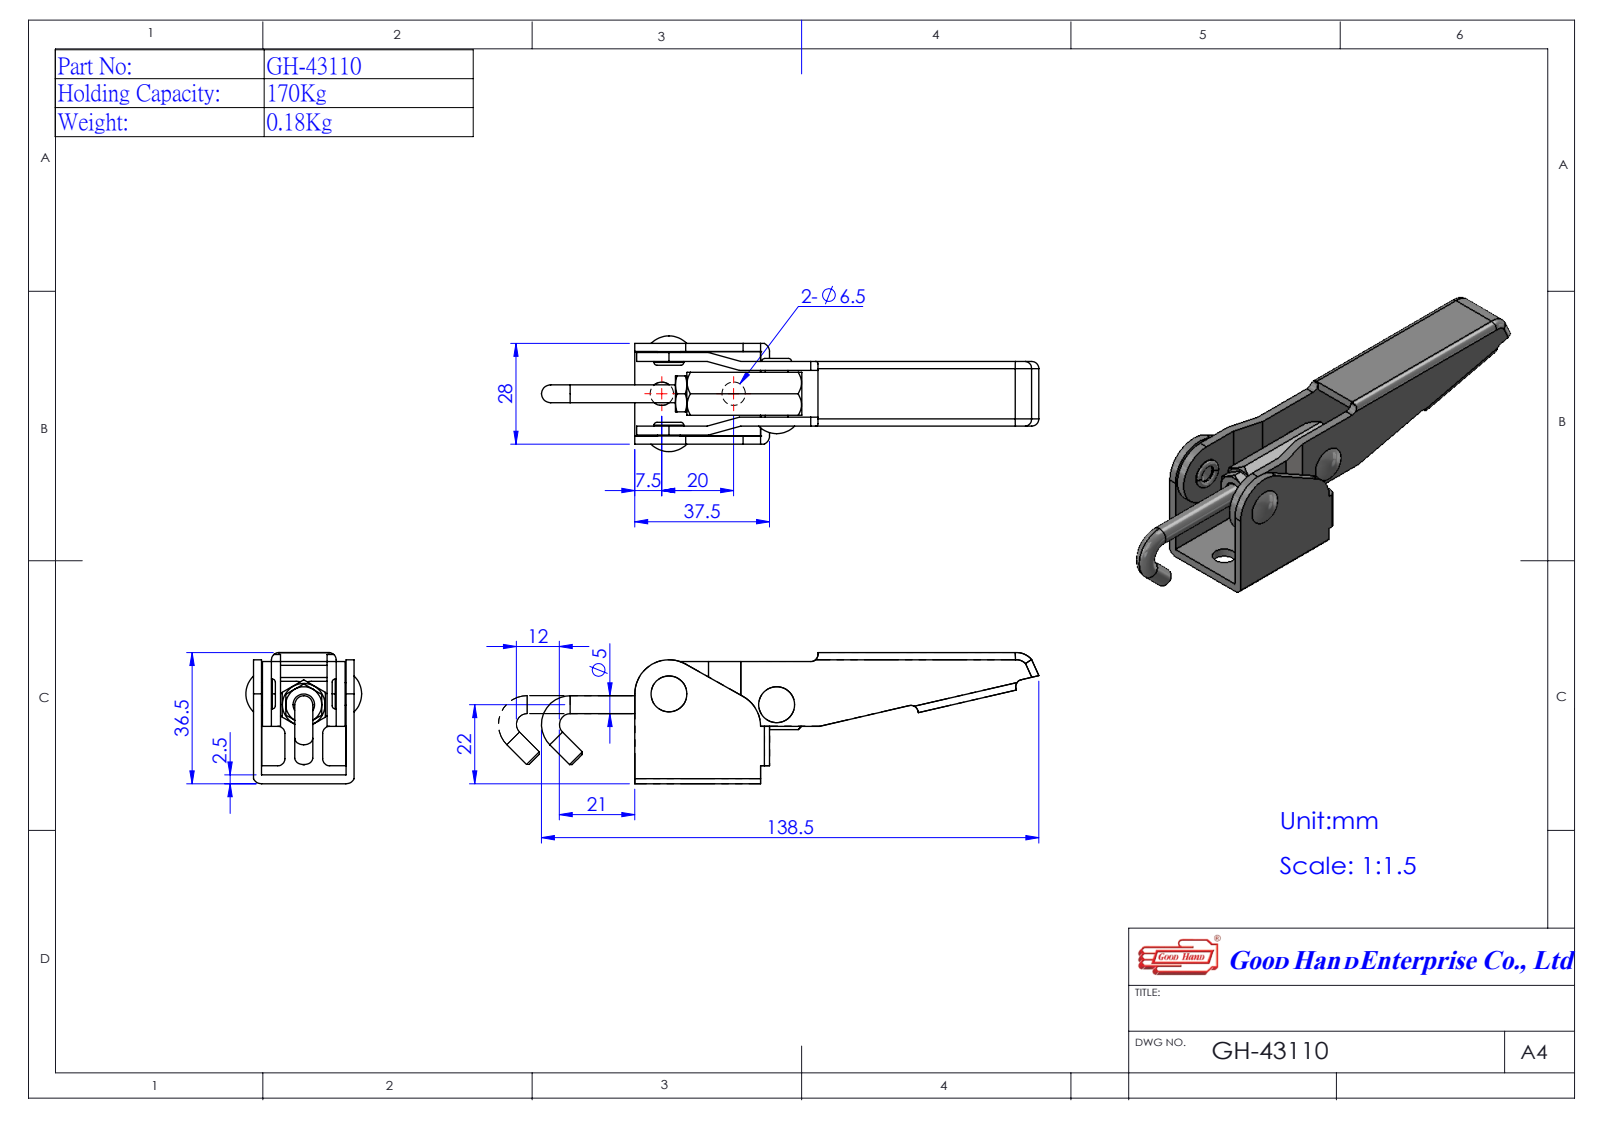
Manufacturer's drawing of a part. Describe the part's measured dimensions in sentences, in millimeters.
The part is named "GH-43110(簡化); 4400144-1^GH-43110(簡化); Group3^GH-43110(簡化); Group2^GH-43110(簡化) (+1 more)". Its 3-D file was written by "SolidWorks 2016 (AUTOMOTIVE_DESIGN)". It is 4 solids with 197 faces: 79 planar, 74 cylindrical and 44 other. Overall it measures 138.49 by 36.51 by 32.2 millimeters. Its volume is 24 524 cubic millimeters and its surface area 20 502 square millimeters. Round holes: 3 of diameter 5, 2 of diameter 6.6, 1 of diameter 6, 1 of diameter 7. Round bosses or shafts: 1 of diameter 8.3, 1 of diameter 6.3, 1 of diameter 5. Partial cylindrical surfaces (rounded edges, fillets, slot ends): 17 of radius 2, 4 of radius 2.51, 2 of radius 9.5, 1 of radius 3.51, 1 of radius 5.51, 1 of radius 9. The main face-to-face distances are 2.5, 20.5, 5, 18, 23, 15.5, 2.75, 5.25, 2.25, 18.25. The hole center spacings are 20, 30.15.
